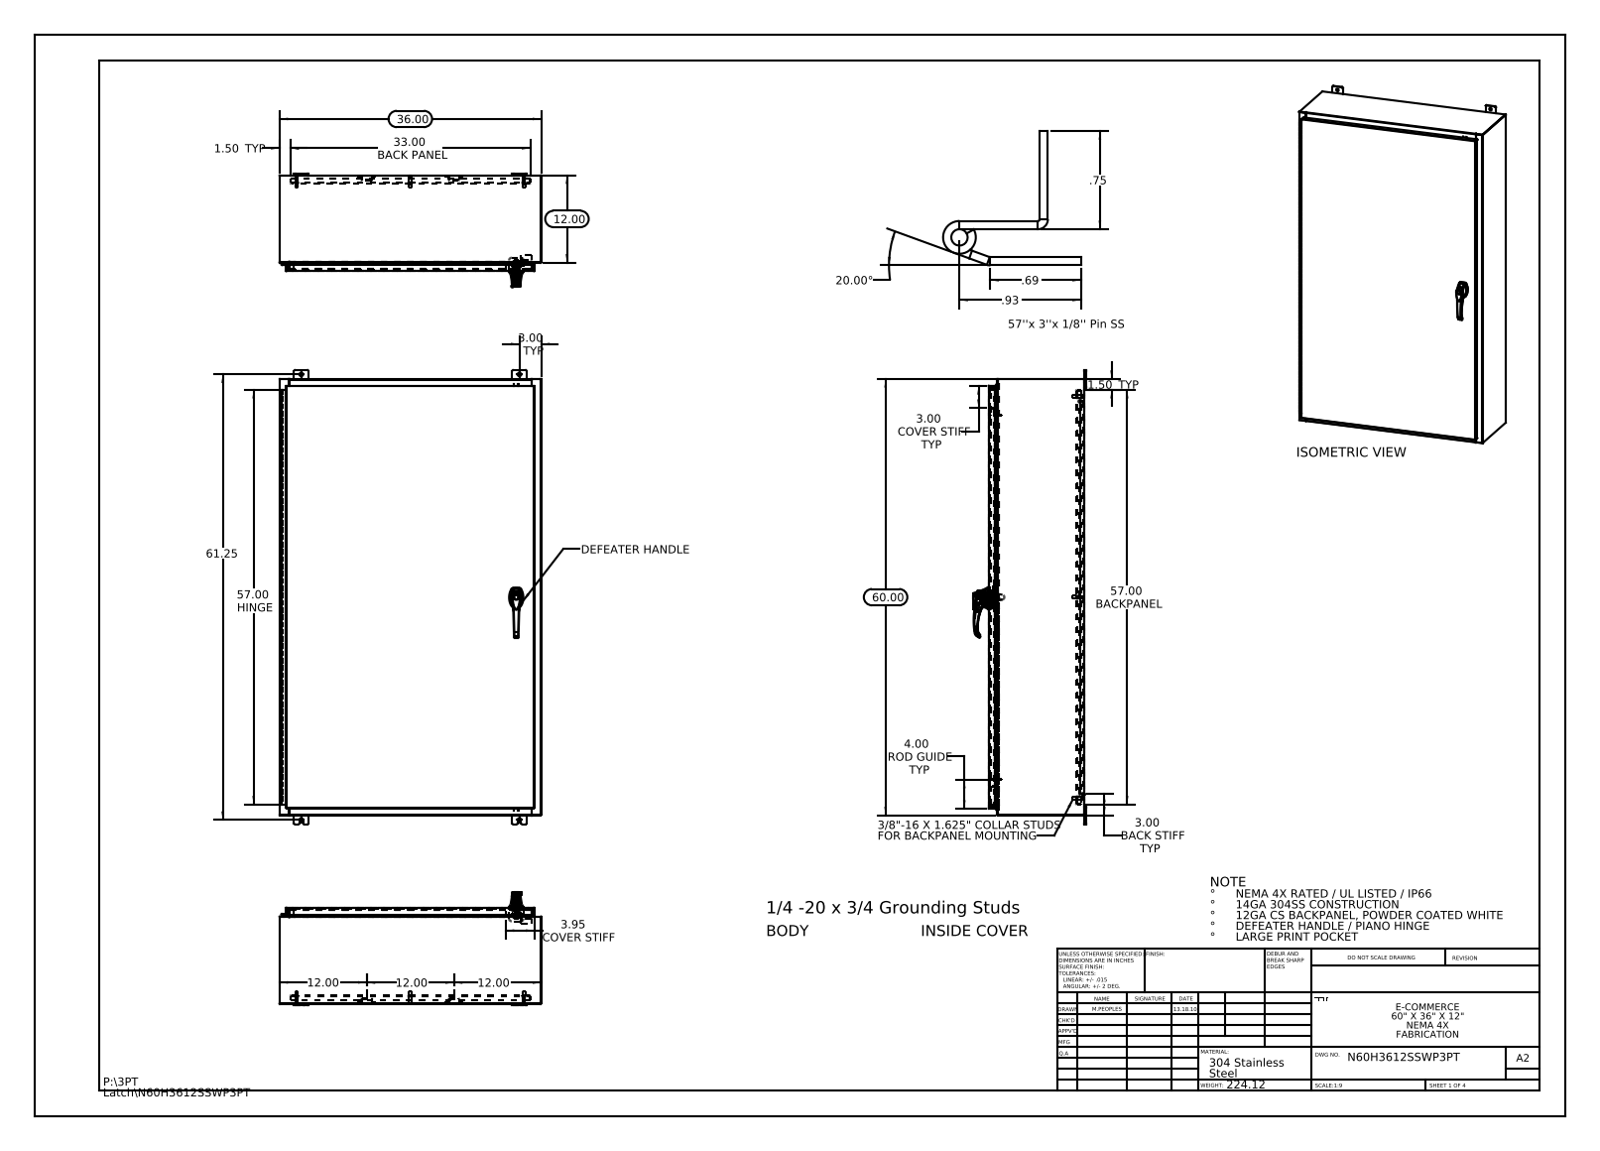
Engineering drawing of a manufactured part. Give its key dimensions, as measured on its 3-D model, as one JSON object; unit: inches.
{"part_name": "2616310101; N60H3612SSWP3PT Top; 033060_032151; N60H3612SSWP3PT Mounting Studs (+8 more)", "step_written_by": "SolidWorks 2013 (CONFIG_CONTROL_DESIGN)", "units": "inches", "bodies": {"solids": 39, "faces": 3512, "planar": 1417, "cylindrical": 1401, "other": 694}, "overall_size": [62.5, 36, 15.495], "volume_in3": 798.3, "surface_area_in2": 19820, "round_holes": [[0.5, 12], [0.25, 10], [0.138, 3], [0.161, 3], [0.079, 2], [0.203, 2], [0.313, 2], [0.437, 2], [0.125, 1], [0.125, 1], [0.197, 1], [0.276, 1]], "round_bosses_or_shafts": [[0.625, 8], [0.375, 8], [0.33, 8], [1.181, 1], [0.748, 1], [0.68, 1], [0.661, 1], [0.639, 1]], "partial_cylinders_radius": [[0.118, 37], [0.013, 34], [0.006, 33], [0.088, 28], [0.19, 24], [0.039, 15], [0.028, 12], [0.008, 6]], "face_to_face_distances": [0.075, 13.126, 13.051, 0.104, 13.201, 1, 12.126, 1.075, 12.051, 1.179], "hole_center_spacings": [23.354, 25.662, 27.625, 41.709, 57.417, 30.975, 31.25, 55.25]}
